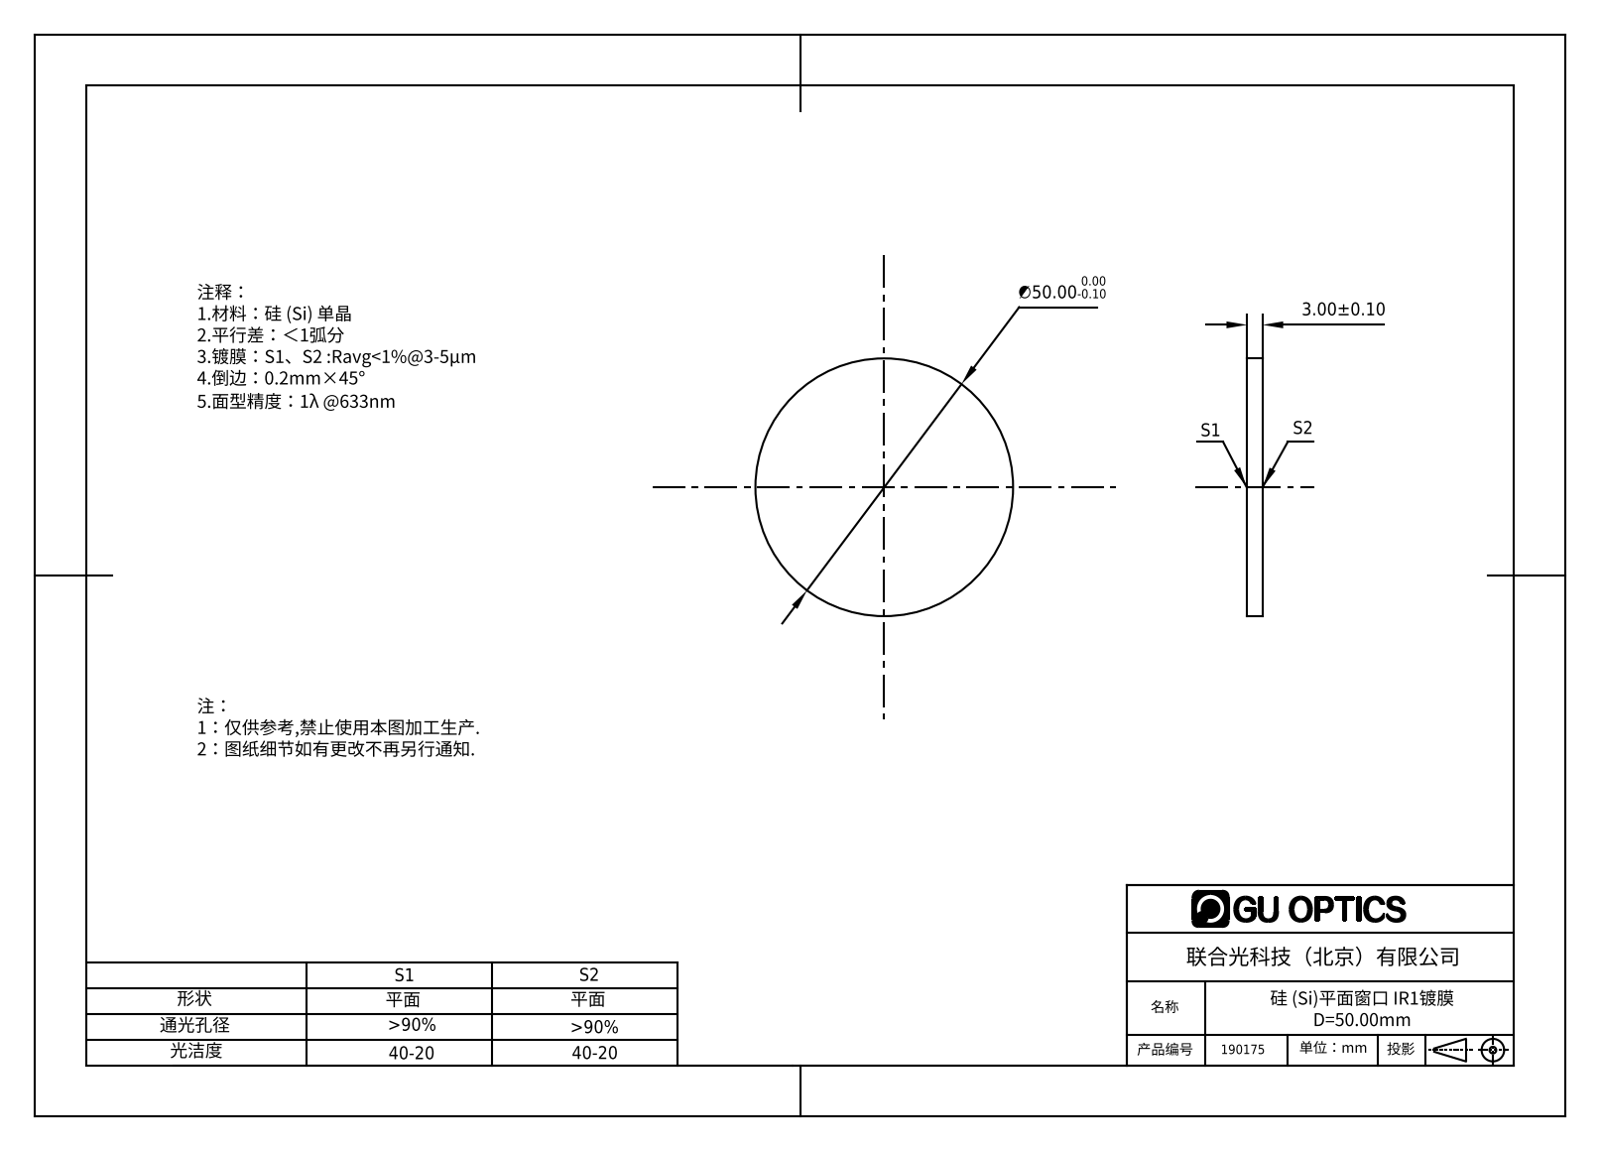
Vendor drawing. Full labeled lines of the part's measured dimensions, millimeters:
Part name (STEP PRODUCT): 190168
STEP written by: SolidWorks 2016 (AUTOMOTIVE_DESIGN)
Units: millimetres
Bodies: 1 solid, 4 faces (2 planar, 2 cylindrical, 0 other)
Overall size (bounding box): 50 × 50 × 3
Volume: 5 890 mm³ · Surface area: 4 398 mm²
Round bosses / shafts (diameter × count): ⌀50 ×1
Main face-to-face distances: 3
